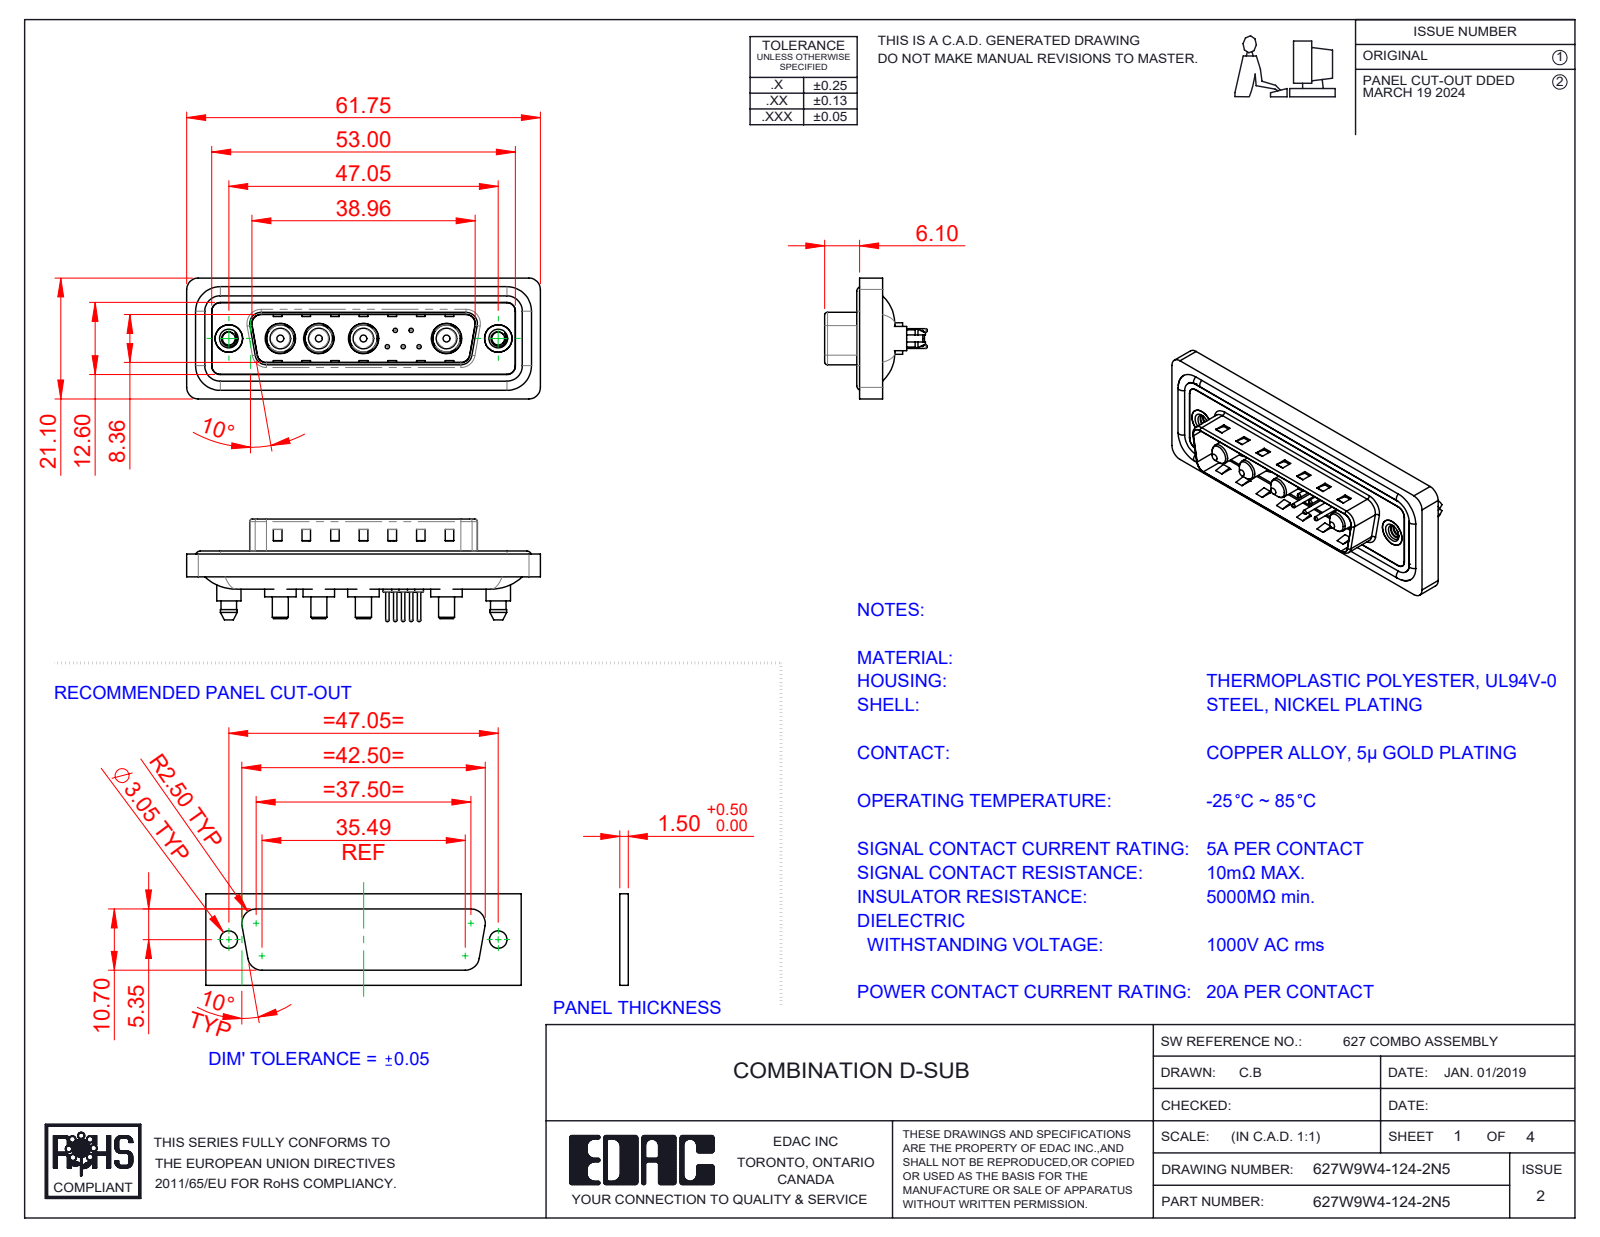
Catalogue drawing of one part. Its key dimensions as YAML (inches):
part_name: "Power Pin_20A S; 627Combo Contact Row 2_24; 627Combo Contact Row 1_24; 627Combo Waterproof Housing_25 Contacts (+5 more)"
step_written_by: "SolidWorks 2023 (CONFIG_CONTROL_DESIGN)"
units: inches
bodies: {solids: 20, faces: 874, planar: 300, cylindrical: 366, other: 208}
overall_size: [2.431, 0.831, 0.705]
volume: 0.46
surface_area: 18.86
round_holes:
  - {diameter: 0.03, count: 5}
  - {diameter: 0.063, count: 5}
  - {diameter: 0.079, count: 5}
  - {diameter: 0.191, count: 4}
  - {diameter: 0.209, count: 4}
  - {diameter: 0.089, count: 2}
  - {diameter: 0.157, count: 2}
  - {diameter: 0.189, count: 2}
  - {diameter: 0.197, count: 2}
round_bosses_or_shafts:
  - {diameter: 0.059, count: 5}
  - {diameter: 0.024, count: 5}
  - {diameter: 0.217, count: 4}
  - {diameter: 0.205, count: 4}
  - {diameter: 0.187, count: 4}
  - {diameter: 0.148, count: 4}
  - {diameter: 0.142, count: 4}
  - {diameter: 0.11, count: 4}
partial_cylinders:
  - {radius: 0.059, count: 24}
  - {radius: 0.079, count: 18}
  - {radius: 0.063, count: 10}
  - {radius: 0.02, count: 8}
  - {radius: 0.01, count: 4}
  - {radius: 0.024, count: 4}
  - {radius: 0.026, count: 4}
  - {radius: 0.035, count: 4}
face_to_face_distances: [0.016, 0.059, 0.043, 0.02, 0.122, 0.063, 0.114, 0.032, 0.377, 0.222]
hole_center_spacings: [0.124, 0.109, 0.198, 0.571, 0.109, 0.173, 0.174, 0.197]
